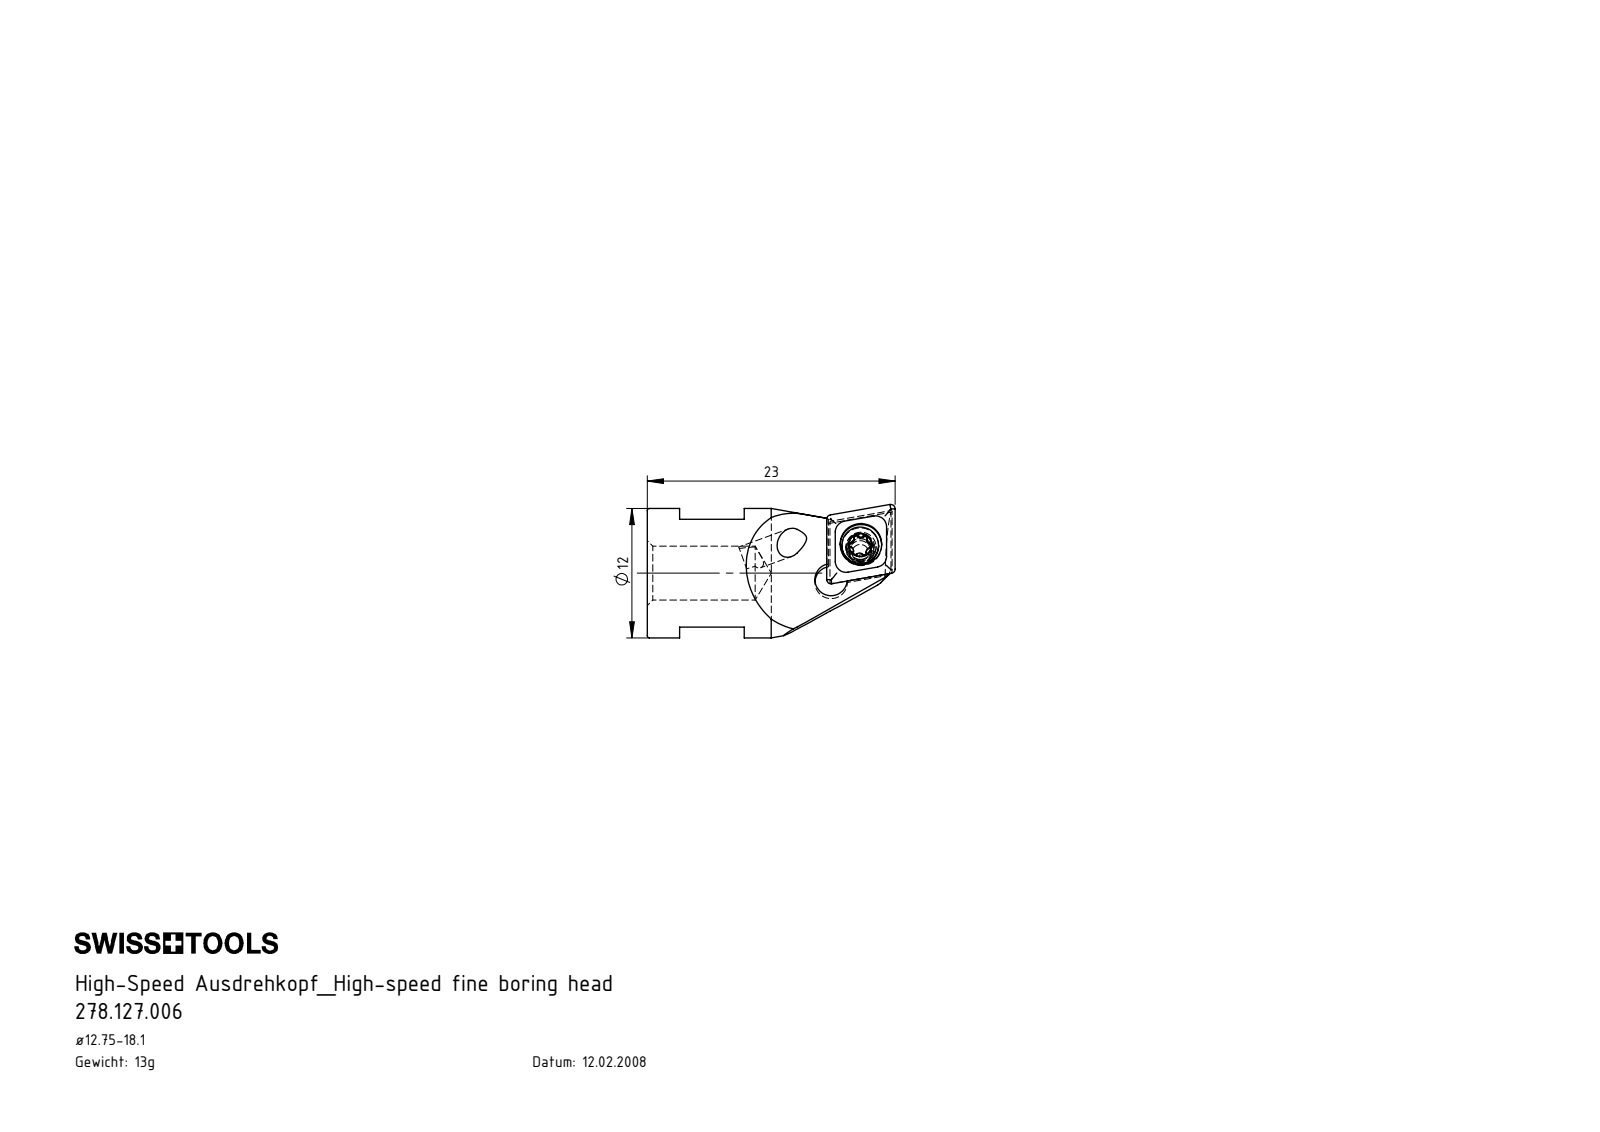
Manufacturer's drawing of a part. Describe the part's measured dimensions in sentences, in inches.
The part is named "WCA-ER2.001.006_A; HS6-A13.K11.023_A; HS6-A13.K11.023; CCMT060204". Its 3-D file was written by "SolidWorks 2015 (CONFIG_CONTROL_DESIGN)". It is 3 solids with 133 faces: 39 planar, 40 cylindrical and 54 other. Overall it measures 0.906 by 0.487 by 0.473 inches. Its volume is 0.094 cubic inches and its surface area 2.041 square inches. Round holes: 1 of diameter 0.081, 1 of diameter 0.098, 1 of diameter 0.11, 1 of diameter 0.152, 1 of diameter 0.197. Round bosses or shafts: 1 of diameter 0.472, 1 of diameter 0.134, 1 of diameter 0.098. Partial cylindrical surfaces (rounded edges, fillets, slot ends): 6 of radius 0.008, 5 of radius 0.014, 4 of radius 0.039, 1 of radius 0.014, 1 of radius 0.055, 1 of radius 0.059, 1 of radius 0.079. The main face-to-face distances are 0.394, 0.09, 0.236, 0.094, 0.354, 0.118, 0.098, 0.102, 0.661, 0.543.
